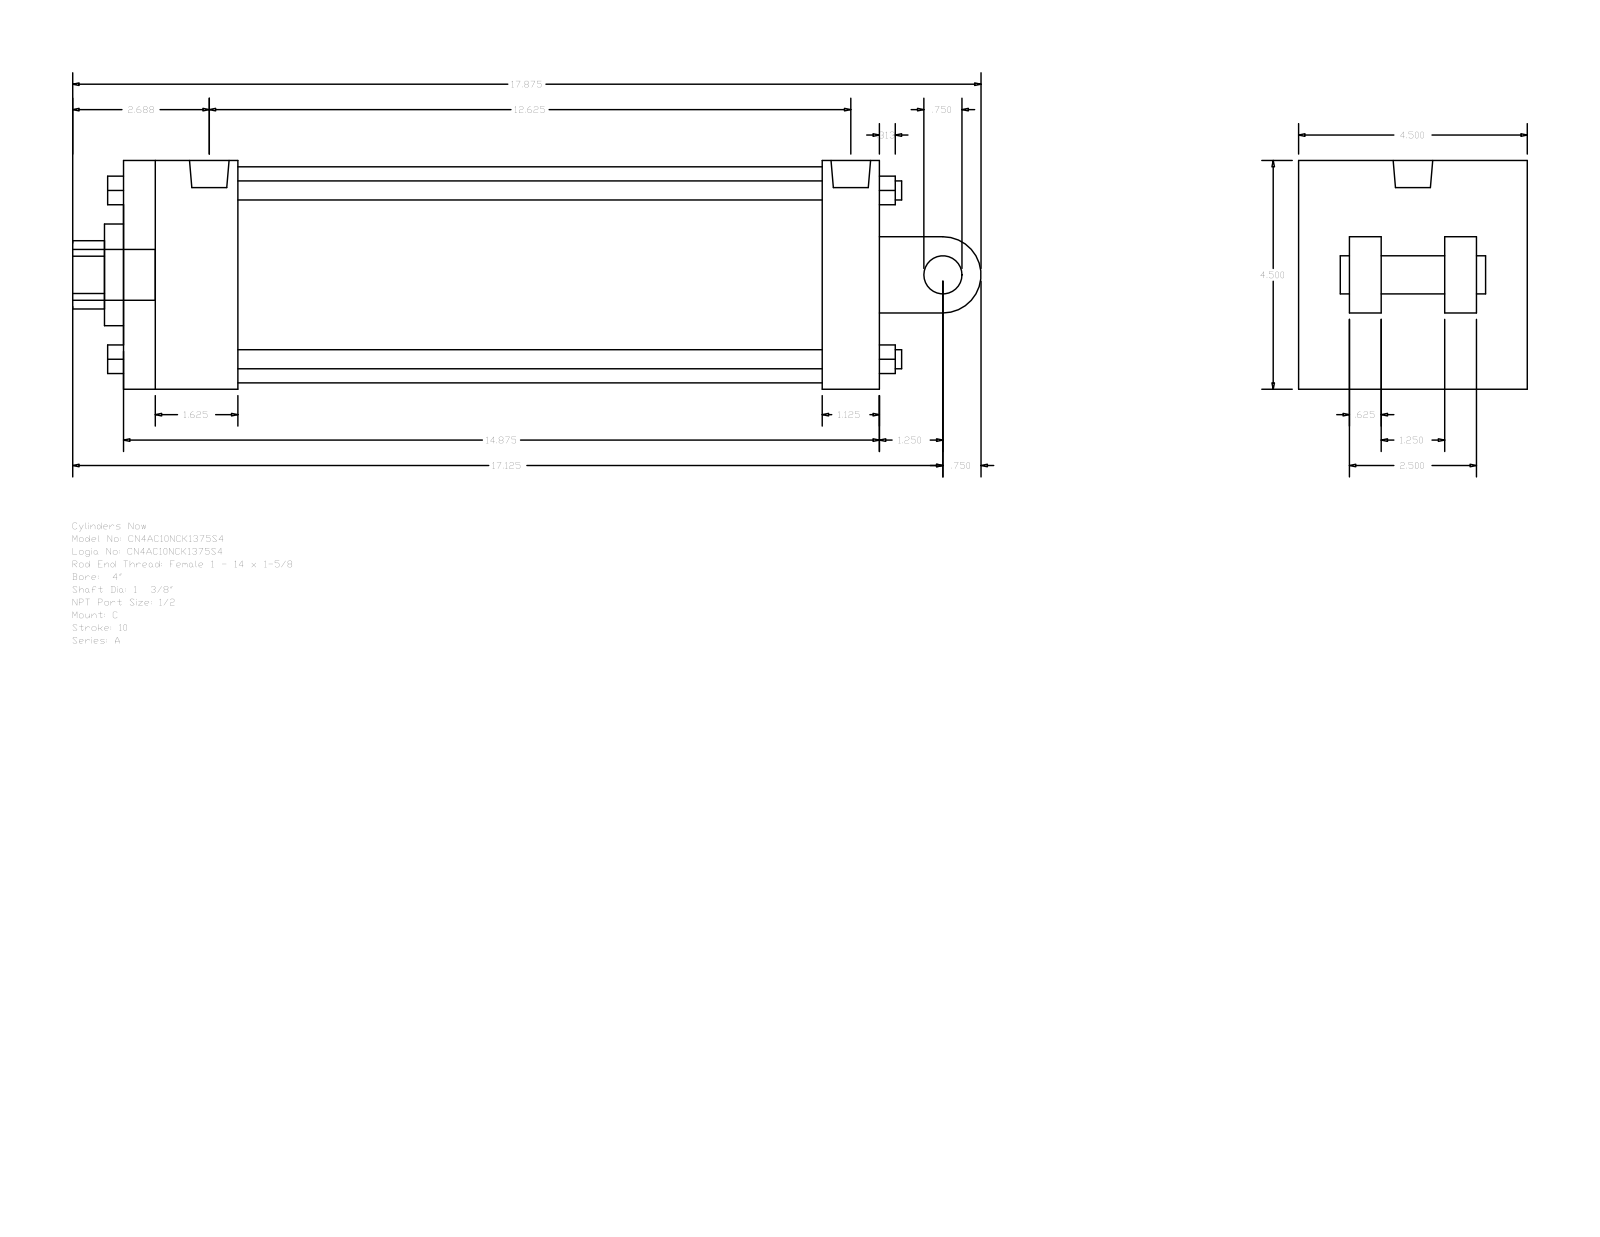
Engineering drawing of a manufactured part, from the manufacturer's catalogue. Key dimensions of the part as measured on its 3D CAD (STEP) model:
Part name (STEP PRODUCT): A_C__0400_1.375
STEP written by: GSSL Pune (CONFIG_CONTROL_DESIGN)
Units: millimetres
Bodies: 0 solids, 135 faces (102 planar, 33 cylindrical, 0 other)
Overall size (bounding box): 454.02 × 114.3 × 114.3
Round holes (diameter × count): ⌀8.73 ×2, ⌀19.77 ×1, ⌀34.92 ×1, ⌀50.8 ×1, ⌀107.95 ×1
Round bosses / shafts (diameter × count): ⌀9.53 ×4, ⌀8.73 ×2, ⌀25.4 ×1, ⌀19.77 ×1, ⌀19.05 ×1
Partial cylindrical surfaces — rounded edges, fillets, slot ends (radius × count): R17.06 ×1, R19.05 ×1
Main face-to-face distances: 114.3, 377.83, 28.58, 73.03, 349.25, 57.15, 292.1, 320.68, 15.87, 41.27
Hole centre spacings: 3.18
